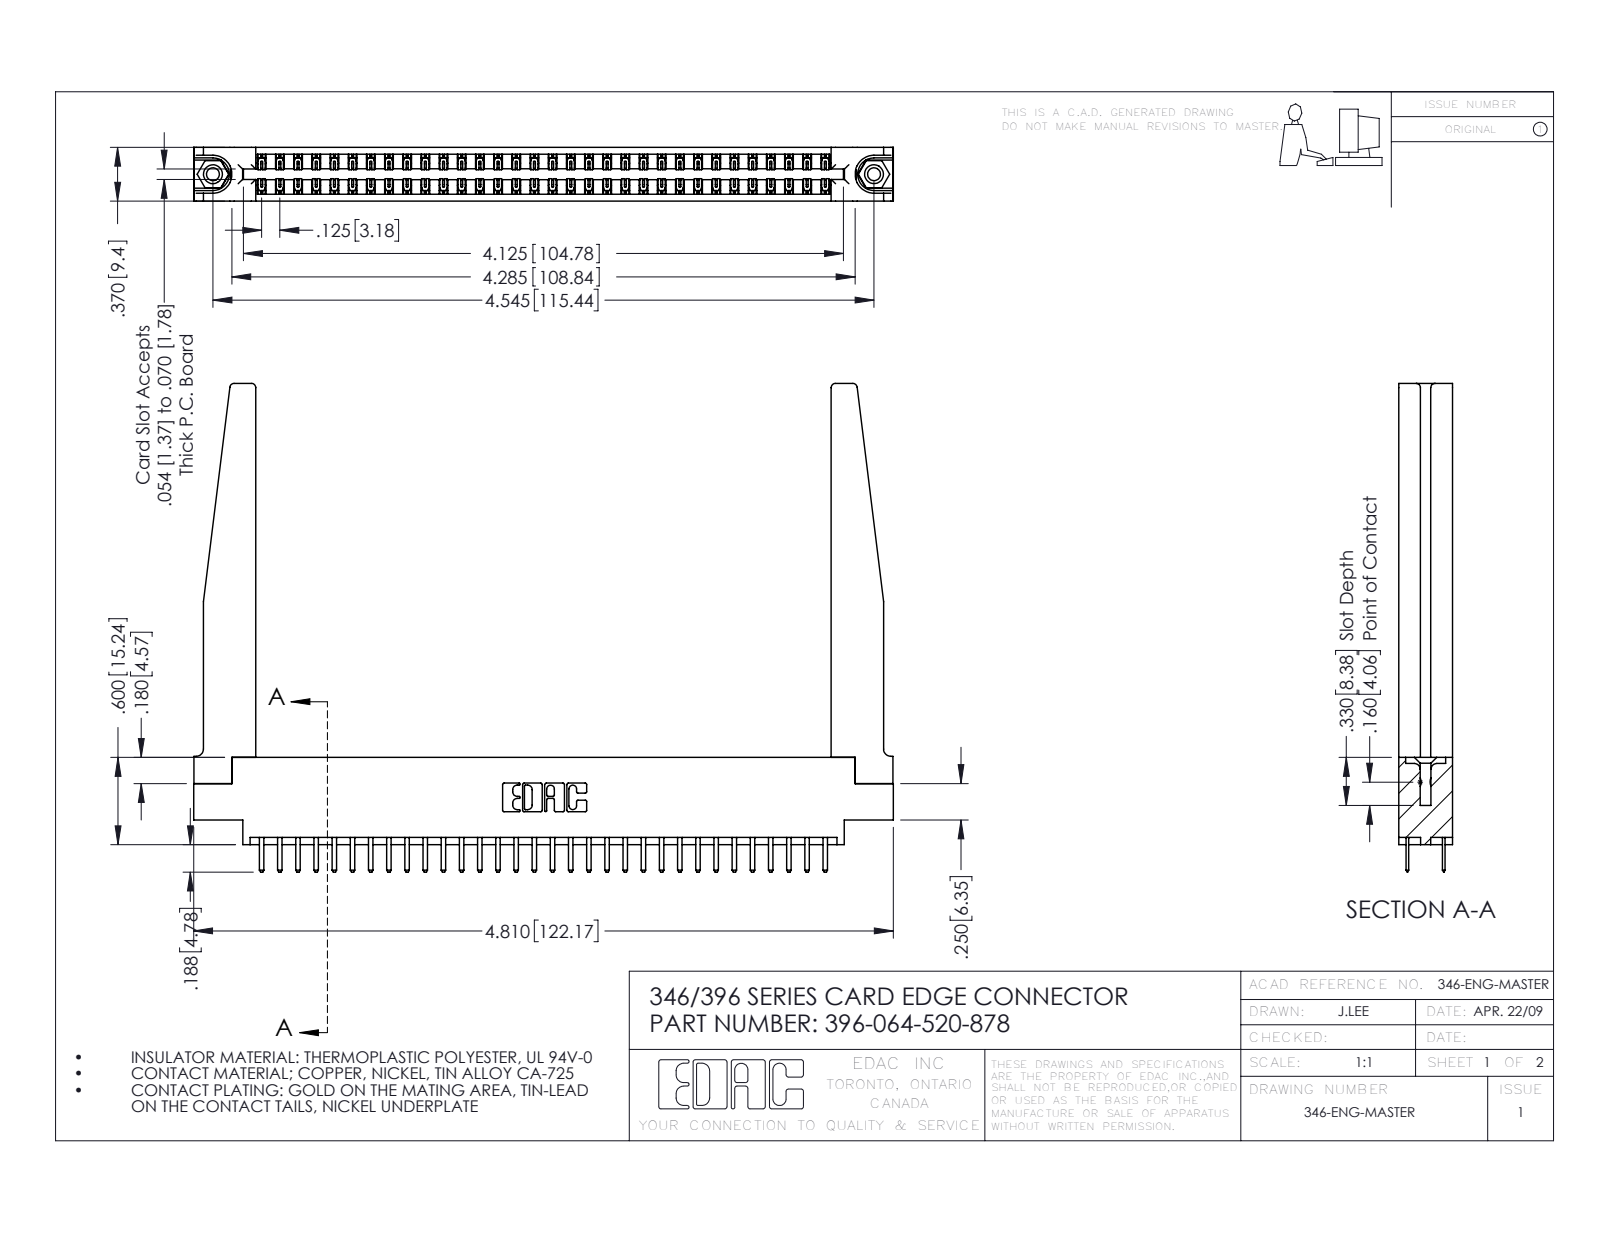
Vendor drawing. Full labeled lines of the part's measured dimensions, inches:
Part name (STEP PRODUCT): 345-292-001_345-293-120; 396-064-520-878; 345-250-001_345-250-001-102; 346 Part_0.170 Offset - 0.156 Dia-TH (+1 more)
STEP written by: SolidWorks 2016 (CONFIG_CONTROL_DESIGN)
Units: inches
Bodies: 69 solids, 3944 faces (2590 planar, 1302 cylindrical, 52 other)
Overall size (bounding box): 4.81 × 3.358 × 0.37
Volume: 1.133 in³ · Surface area: 34.89 in²
Round holes (diameter × count): ⌀0.089 ×2, ⌀0.125 ×2, ⌀0.156 ×2, ⌀0.064 ×1
Round bosses / shafts (diameter × count): ⌀0.155 ×2
Partial cylindrical surfaces — rounded edges, fillets, slot ends (radius × count): R0.006 ×96, R0.01 ×68, R0.01 ×22, R0.03 ×8, R0.007 ×6, R0.031 ×6, R0.026 ×3, R0.014 ×2
Main face-to-face distances: 0.37, 0.048, 0.322, 0.072, 0.25, 0.148, 0.15, 0.298, 0.025, 0.275
Hole centre spacings: 0.246, 4.337, 4.545
